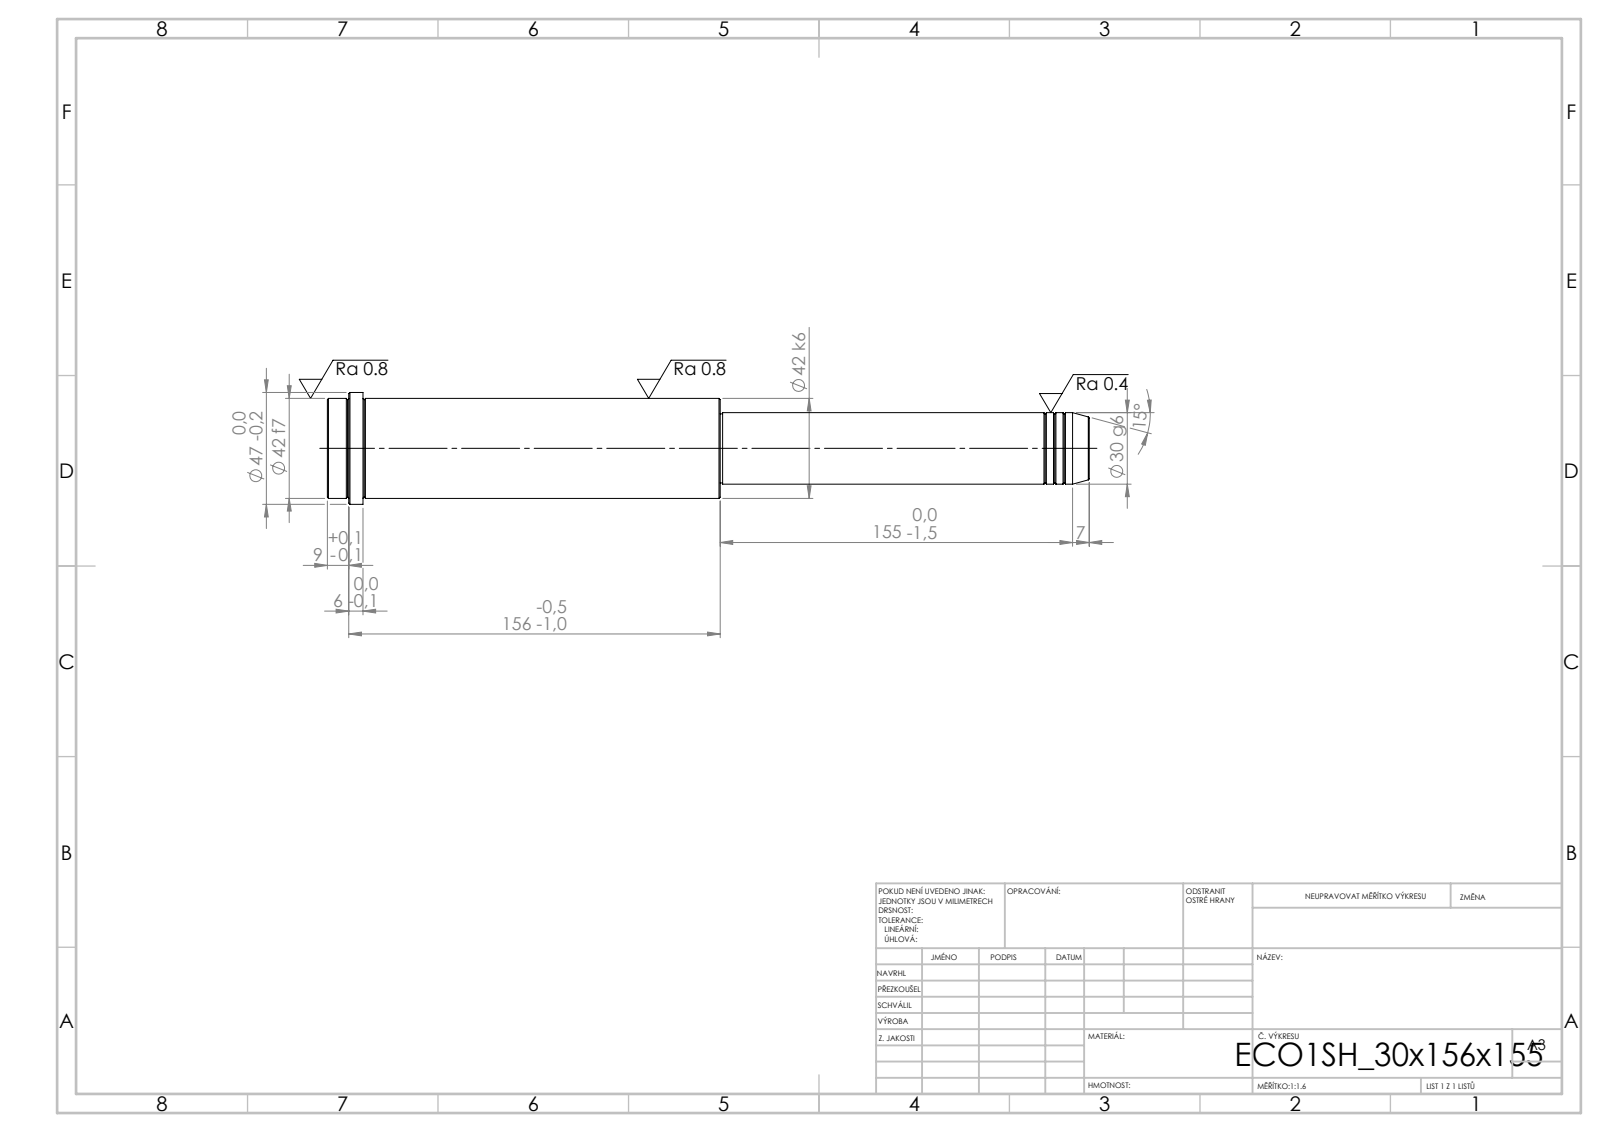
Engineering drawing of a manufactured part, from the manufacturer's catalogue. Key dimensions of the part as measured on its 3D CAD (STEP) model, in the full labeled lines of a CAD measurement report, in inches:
STEP written by: SolidWorks 2019 (CONFIG_CONTROL_DESIGN)
Units: inches
Bodies: 1 solid, 52 faces (6 planar, 16 cylindrical, 30 other)
Overall size (bounding box): 12.598 × 1.85 × 1.85
Volume: 20.71 in³ · Surface area: 62.02 in²
Round bosses / shafts (diameter × count): ⌀1.85 ×1, ⌀1.654 ×1, ⌀1.181 ×1, ⌀1.142 ×1
Main face-to-face distances: 6.496, 6.102, 12.598, 12.008, 5.906, 0.591, 12.244, 6.142, 0.236, 0.354
